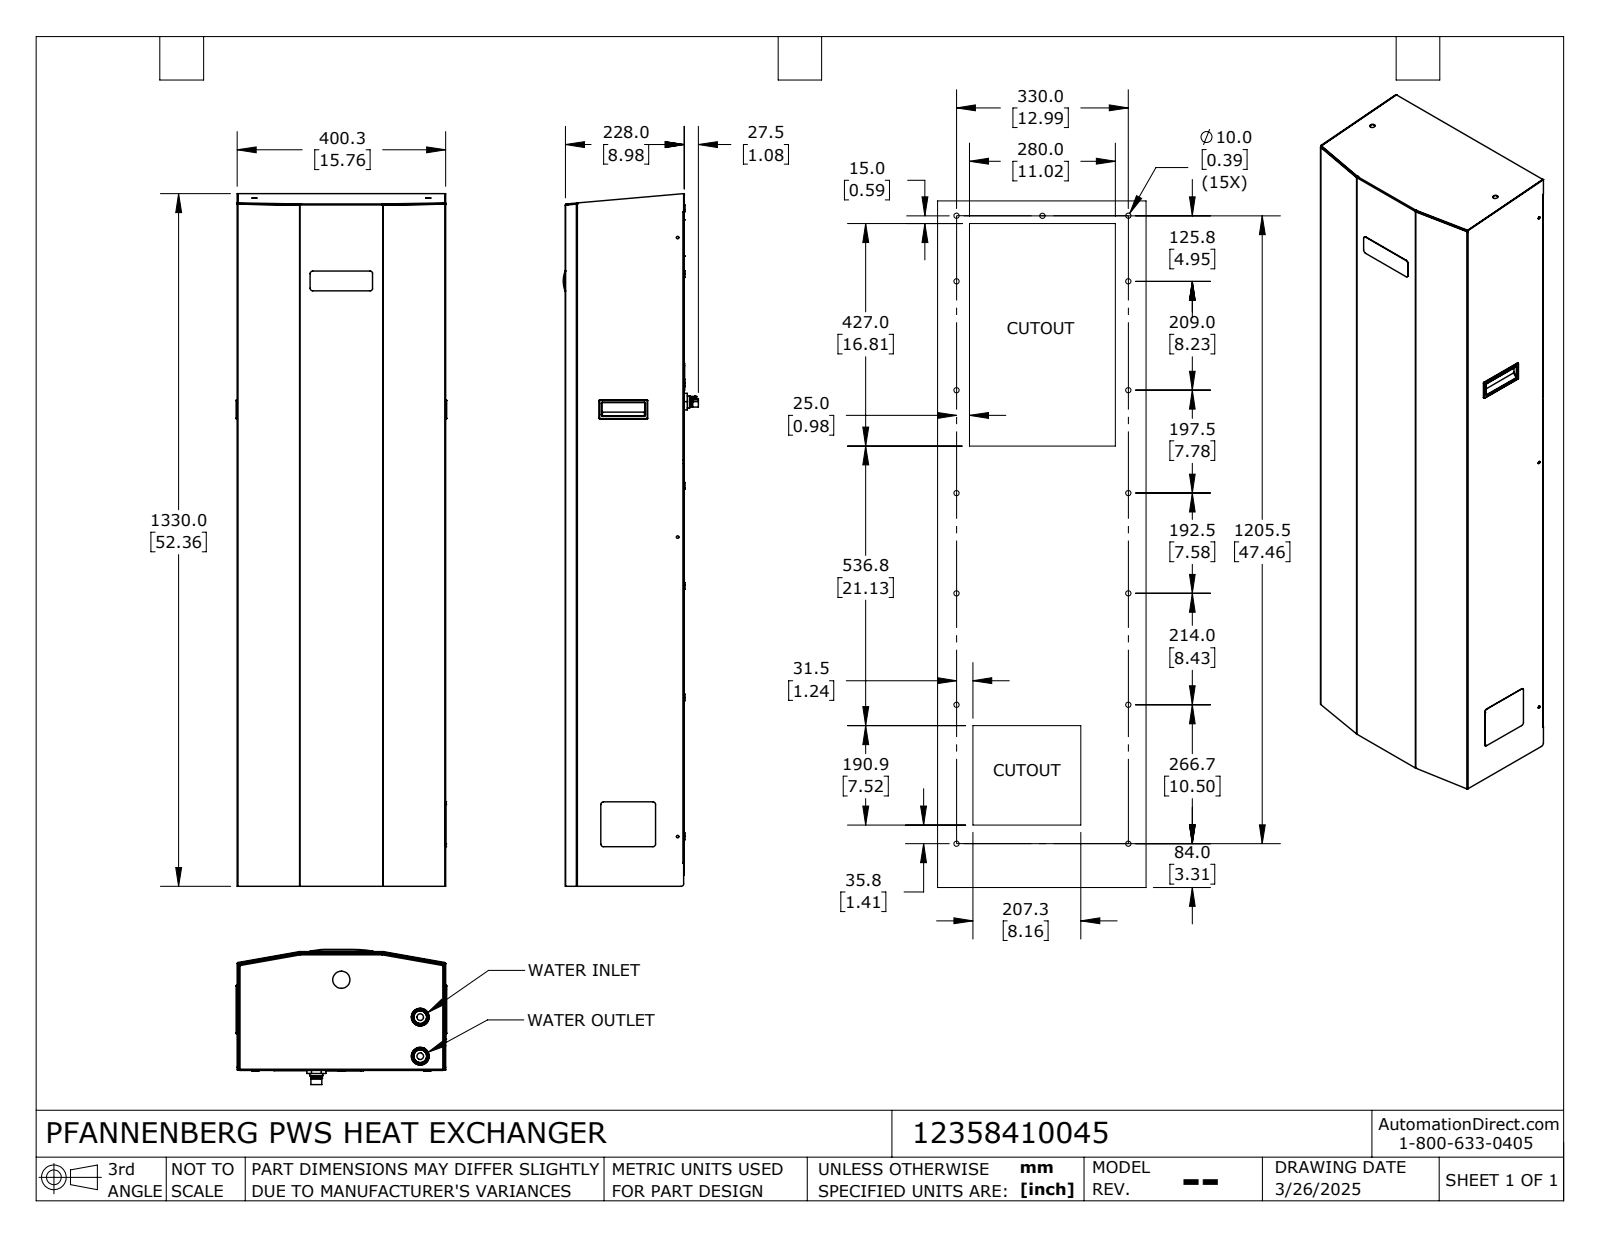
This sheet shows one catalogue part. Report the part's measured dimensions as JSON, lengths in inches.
{"part_name": "12358410045_Default", "step_written_by": "SolidWorks 2024 (CONFIG_CONTROL_DESIGN)", "units": "inches", "bodies": {"solids": 11, "faces": 1571, "planar": 794, "cylindrical": 656, "other": 121}, "overall_size": [52.362, 15.917, 10.23], "volume_in3": 6725, "surface_area_in2": 7865, "round_holes": [[0.165, 19], [0.283, 15], [0.197, 6], [0.169, 5], [0.209, 5], [0.189, 3], [0.472, 3], [0.394, 2], [0.5, 2], [0.591, 2], [0.992, 2], [1, 2]], "round_bosses_or_shafts": [[0.512, 15], [0.079, 4], [0.984, 2], [0.965, 2], [0.571, 2], [1.102, 1], [0.906, 1]], "partial_cylinders_radius": [[0.125, 112], [0.039, 52], [0.031, 20], [0.198, 15], [0.197, 13], [0.087, 11], [0.076, 7], [0.047, 4]], "face_to_face_distances": [0.045, 15.714, 0.166, 15.504, 15.548, 0.211, 0.056, 0.031, 0.087, 15.669], "hole_center_spacings": [0.294, 2.86, 3.547, 4.398, 6.911, 7.222, 0.244, 6]}
